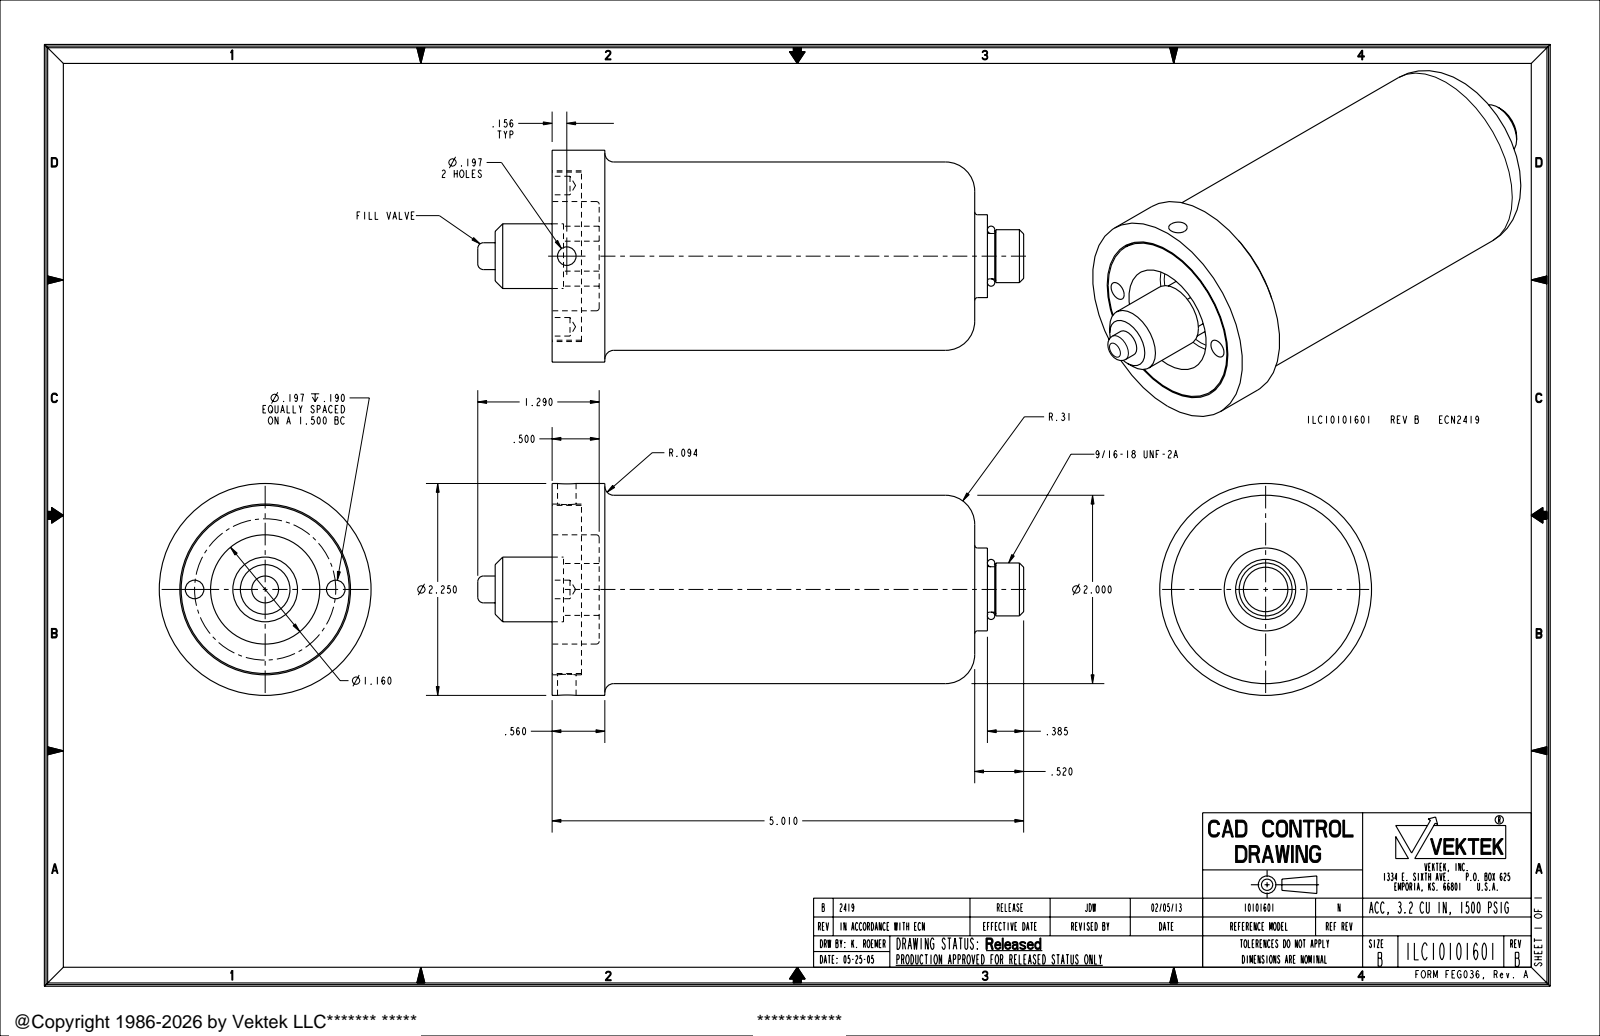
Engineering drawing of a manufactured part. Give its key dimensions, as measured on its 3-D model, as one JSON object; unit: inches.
{"part_name": "ILC10101601", "step_written_by": "PRO/ENGINEER BY PARAMETRIC TECHNOLOGY CORPORATION, 2007460 (AUTOMOTIVE_DESIGN_CC2)", "units": "inches", "bodies": {"solids": 2, "faces": 72, "planar": 18, "cylindrical": 28, "other": 26}, "overall_size": [5.8, 2.25, 2.25], "volume_in3": 14.44, "surface_area_in2": 45.19, "round_holes": [[0.197, 3], [1.16, 1], [1.813, 1]], "round_bosses_or_shafts": [[2.25, 1], [2, 1], [1.785, 1], [0.88, 1], [0.687, 1], [0.562, 1], [0.482, 1], [0.285, 1]], "face_to_face_distances": [4.49, 3.99, 0.5, 0.135, 4.125, 4.625, 0.551, 4.065, 3.93, 0.06], "hole_center_spacings": [0.75, 1.5]}
